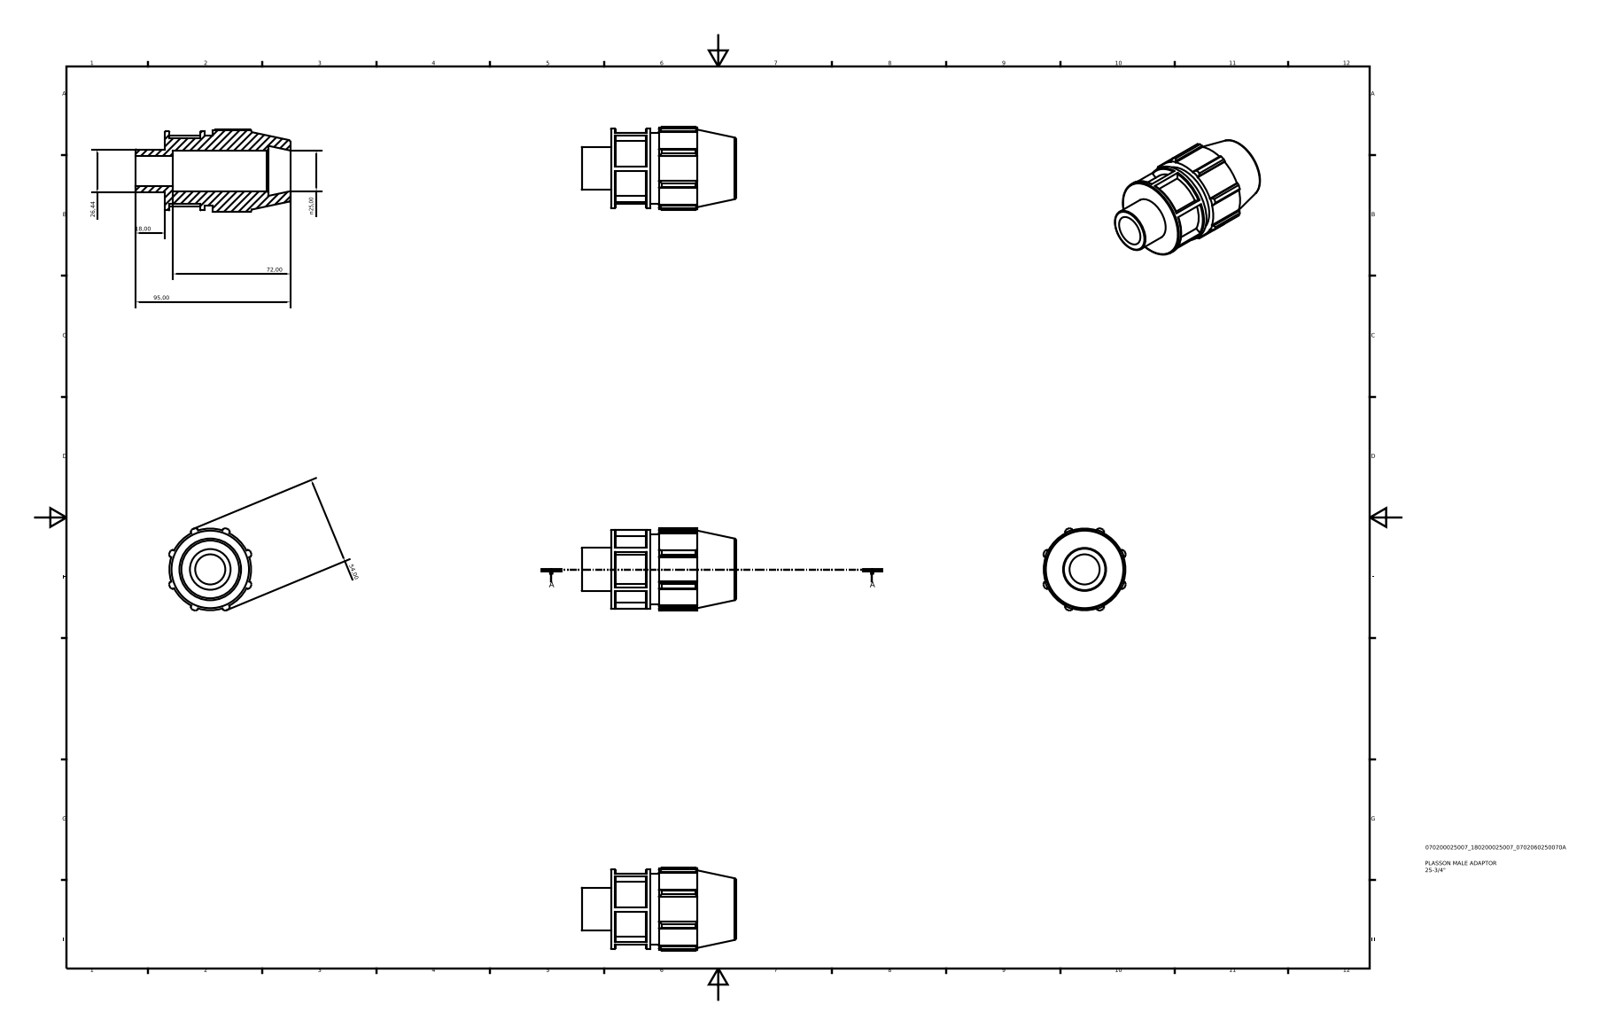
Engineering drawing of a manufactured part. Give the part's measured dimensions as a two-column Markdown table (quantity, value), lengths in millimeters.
| quantity | value |
| --- | --- |
| part name | 070200025007_180200025007 |
| STEP written by | Autodesk Inventor 2015 (AUTOMOTIVE_DESIGN) |
| units | millimeters |
| bodies | 1 solid, 117 faces (63 planar, 27 cylindrical, 27 other) |
| overall size | 95 × 50.81 × 50.81 |
| volume | 92 111 mm³ |
| surface area | 25 615 mm² |
| round holes (diameter × count) | 18.51 × 1, 25 × 1 |
| round bosses / shafts (diameter × count) | 48.6 × 1, 43.2 × 1, 40.5 × 1, 26.44 × 1 |
| partial cylindrical surfaces (radius × count) | 25.11 × 1, 27 × 1 |
| main face-to-face distances | 47.5, 29.5, 77, 2.7, 2.71, 26.79, 74.29, 21.71, 19, 7.79 |
